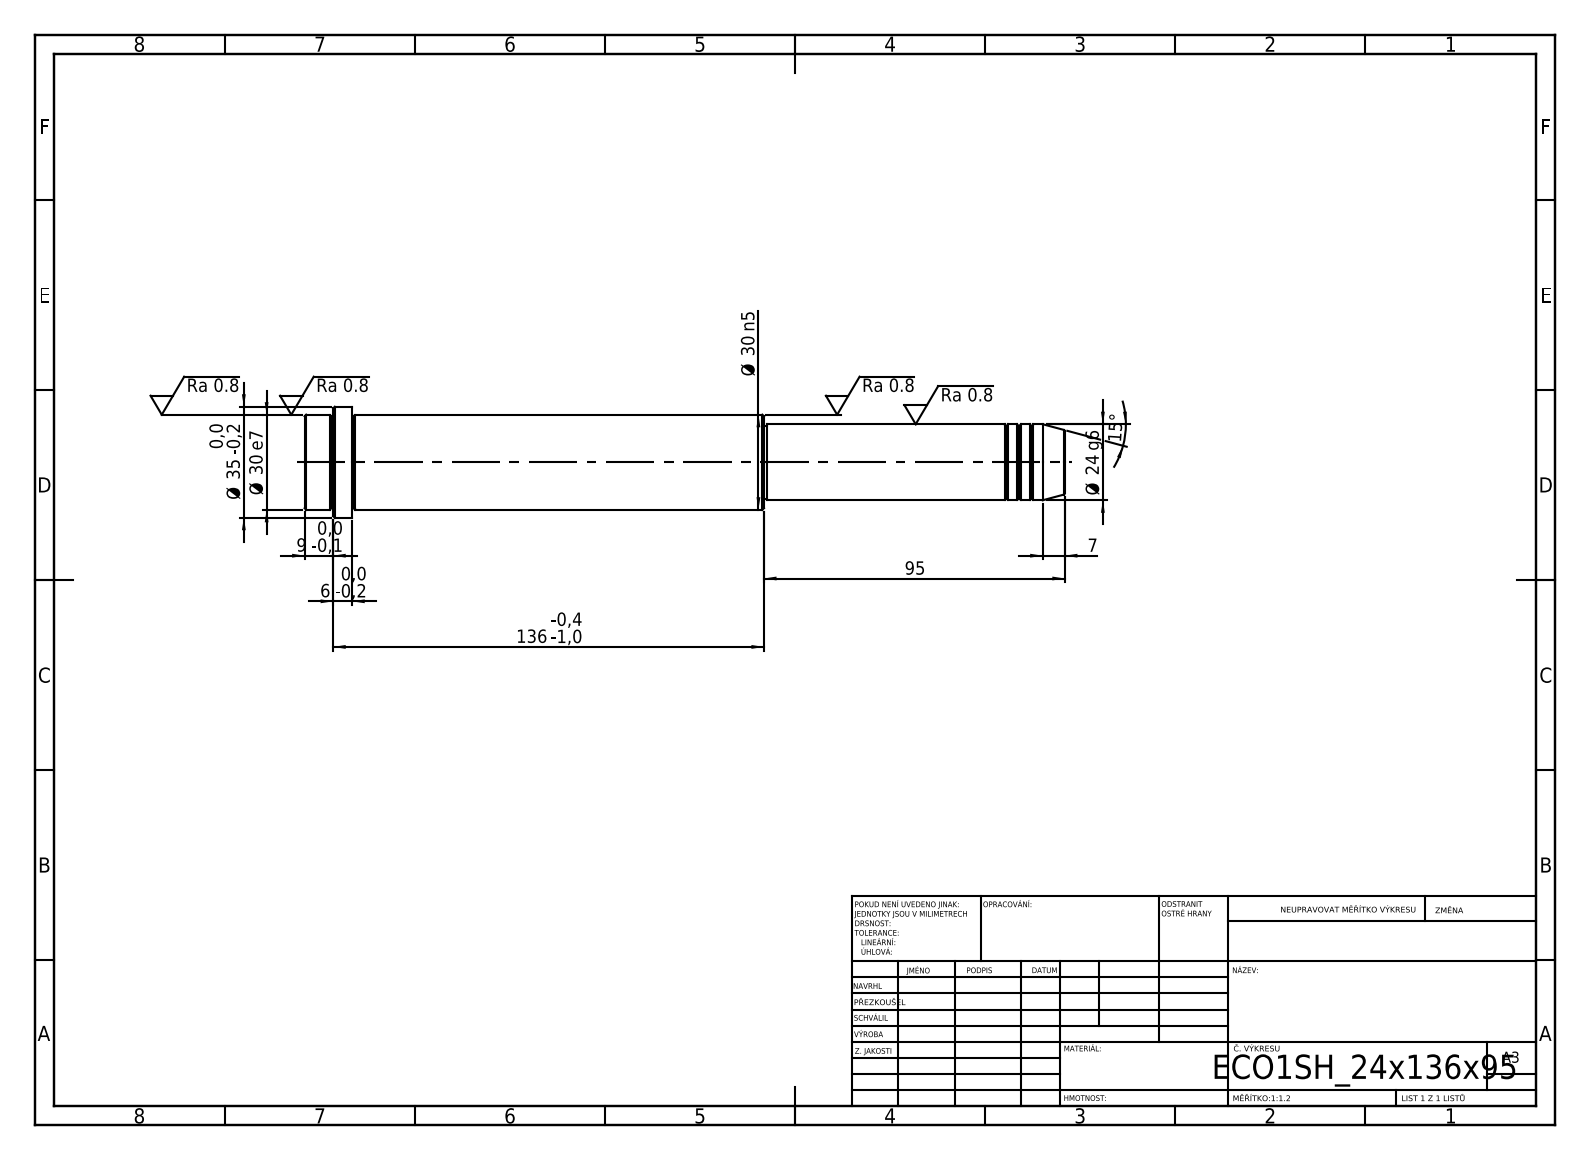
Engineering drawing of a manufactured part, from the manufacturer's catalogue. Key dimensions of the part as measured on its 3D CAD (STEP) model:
STEP written by: SolidWorks 2019 (CONFIG_CONTROL_DESIGN)
Units: millimetres
Bodies: 1 solid, 52 faces (6 planar, 16 cylindrical, 30 other)
Overall size (bounding box): 240 × 35 × 35
Volume: 146 298 mm³ · Surface area: 22 889 mm²
Round bosses / shafts (diameter × count): ⌀35 ×1, ⌀30 ×1, ⌀24 ×1, ⌀23 ×1
Main face-to-face distances: 240, 225, 15, 95, 130, 145, 231, 136, 6, 9
